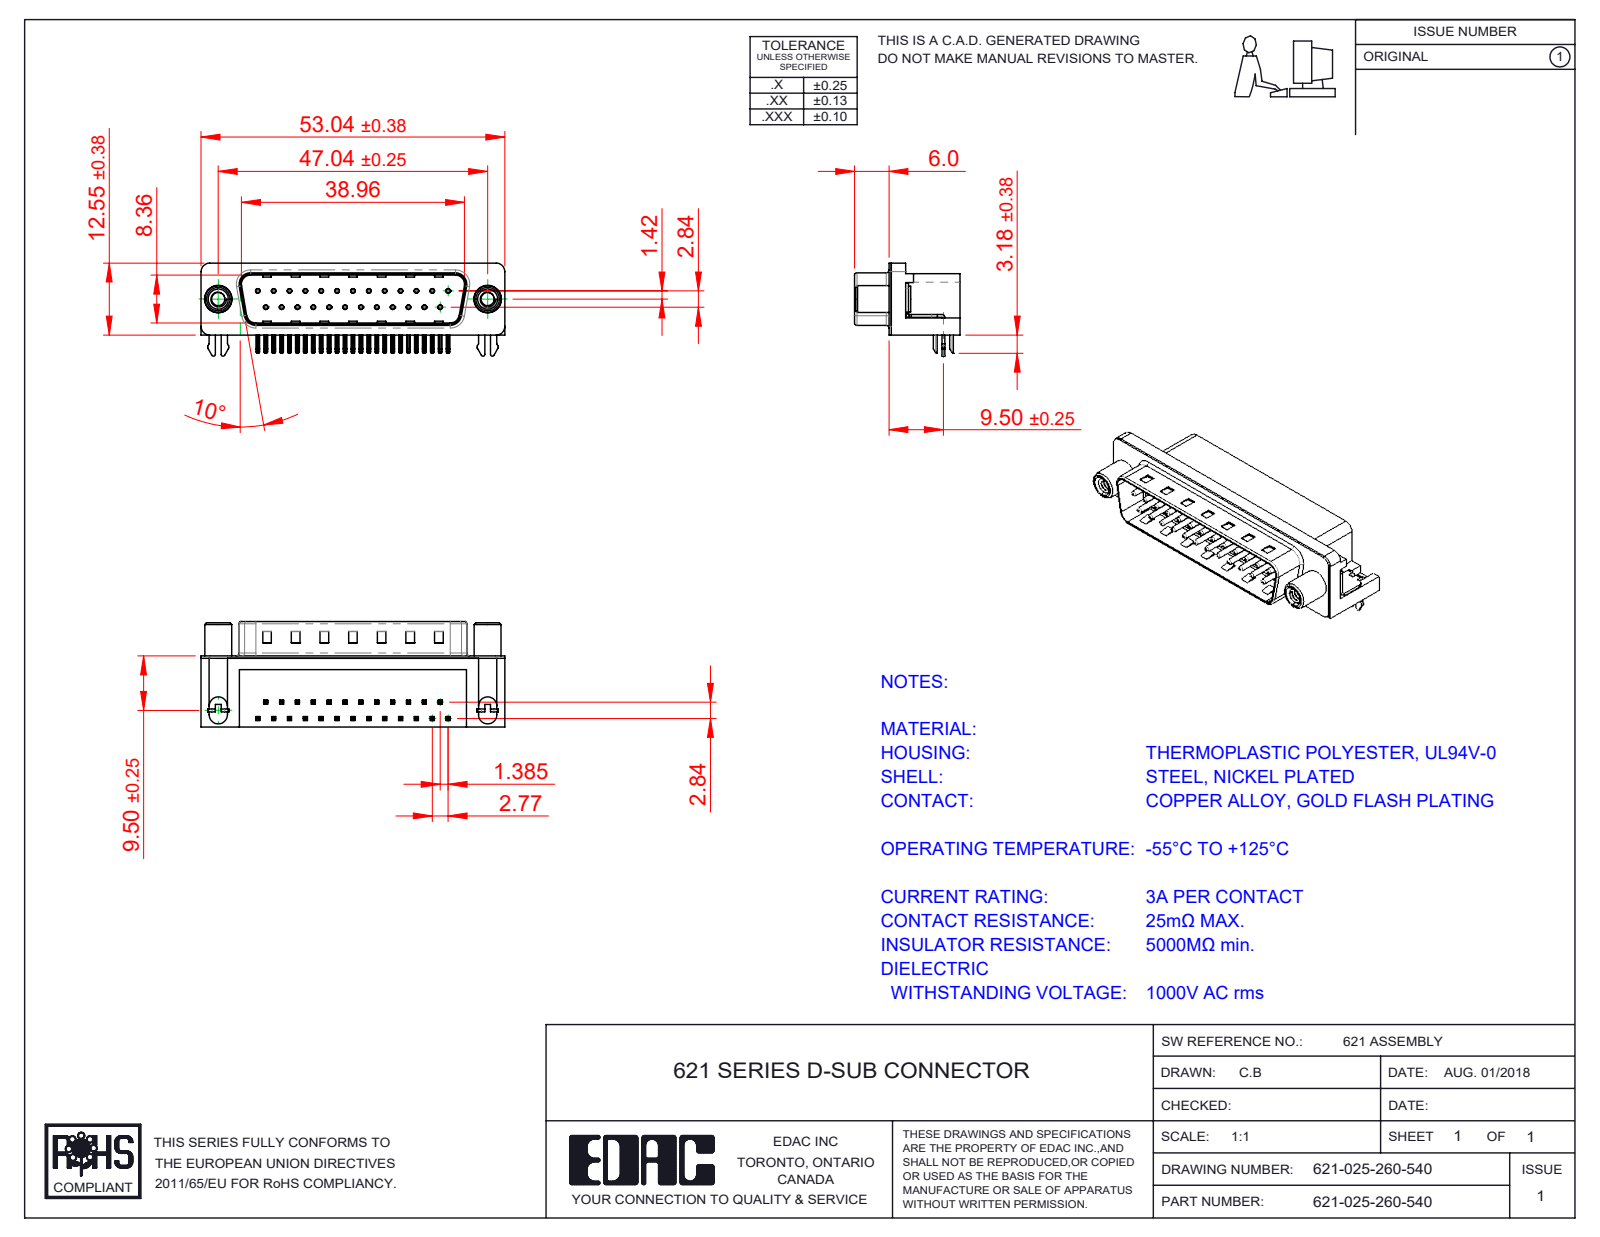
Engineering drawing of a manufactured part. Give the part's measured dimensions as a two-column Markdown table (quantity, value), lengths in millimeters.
| quantity | value |
| --- | --- |
| part name | 621 Contact Bottom; 621 Shell_25 Socket; 621 Contact Top; 621 Housing_25 Socket (+3 more) |
| STEP written by | SolidWorks 2016 (CONFIG_CONTROL_DESIGN) |
| units | millimeters |
| bodies | 31 solids, 2377 faces (1439 planar, 673 cylindrical, 265 other) |
| overall size | 53.04 × 18.4 × 16.25 |
| volume | 6 448 mm³ |
| surface area | 7 957 mm² |
| round holes (diameter × count) | 0.35 × 25, 0.8 × 25, 2 × 2, 2.3 × 2, 3.1 × 2, 4 × 2, 4.8 × 2, 5 × 2 |
| round bosses / shafts (diameter × count) | 0.75 × 25, 4.9 × 2, 4.7 × 2, 4.5 × 2, 3.85 × 2, 3 × 2 |
| partial cylindrical surfaces (radius × count) | 0.25 × 104, 0.12 × 50, 1 × 16, 0.5 × 9, 1.6 × 8, 1.5 × 7, 0.9 × 4, 2 × 4 |
| main face-to-face distances | 0.4, 12, 10.35, 2.1, 8.76, 10.46, 1.7, 10.86, 12.4, 2.9 |
| hole center spacings | 3.16, 2.77, 5.54, 8.31, 11.08, 13.85, 16.62, 5.03 |
